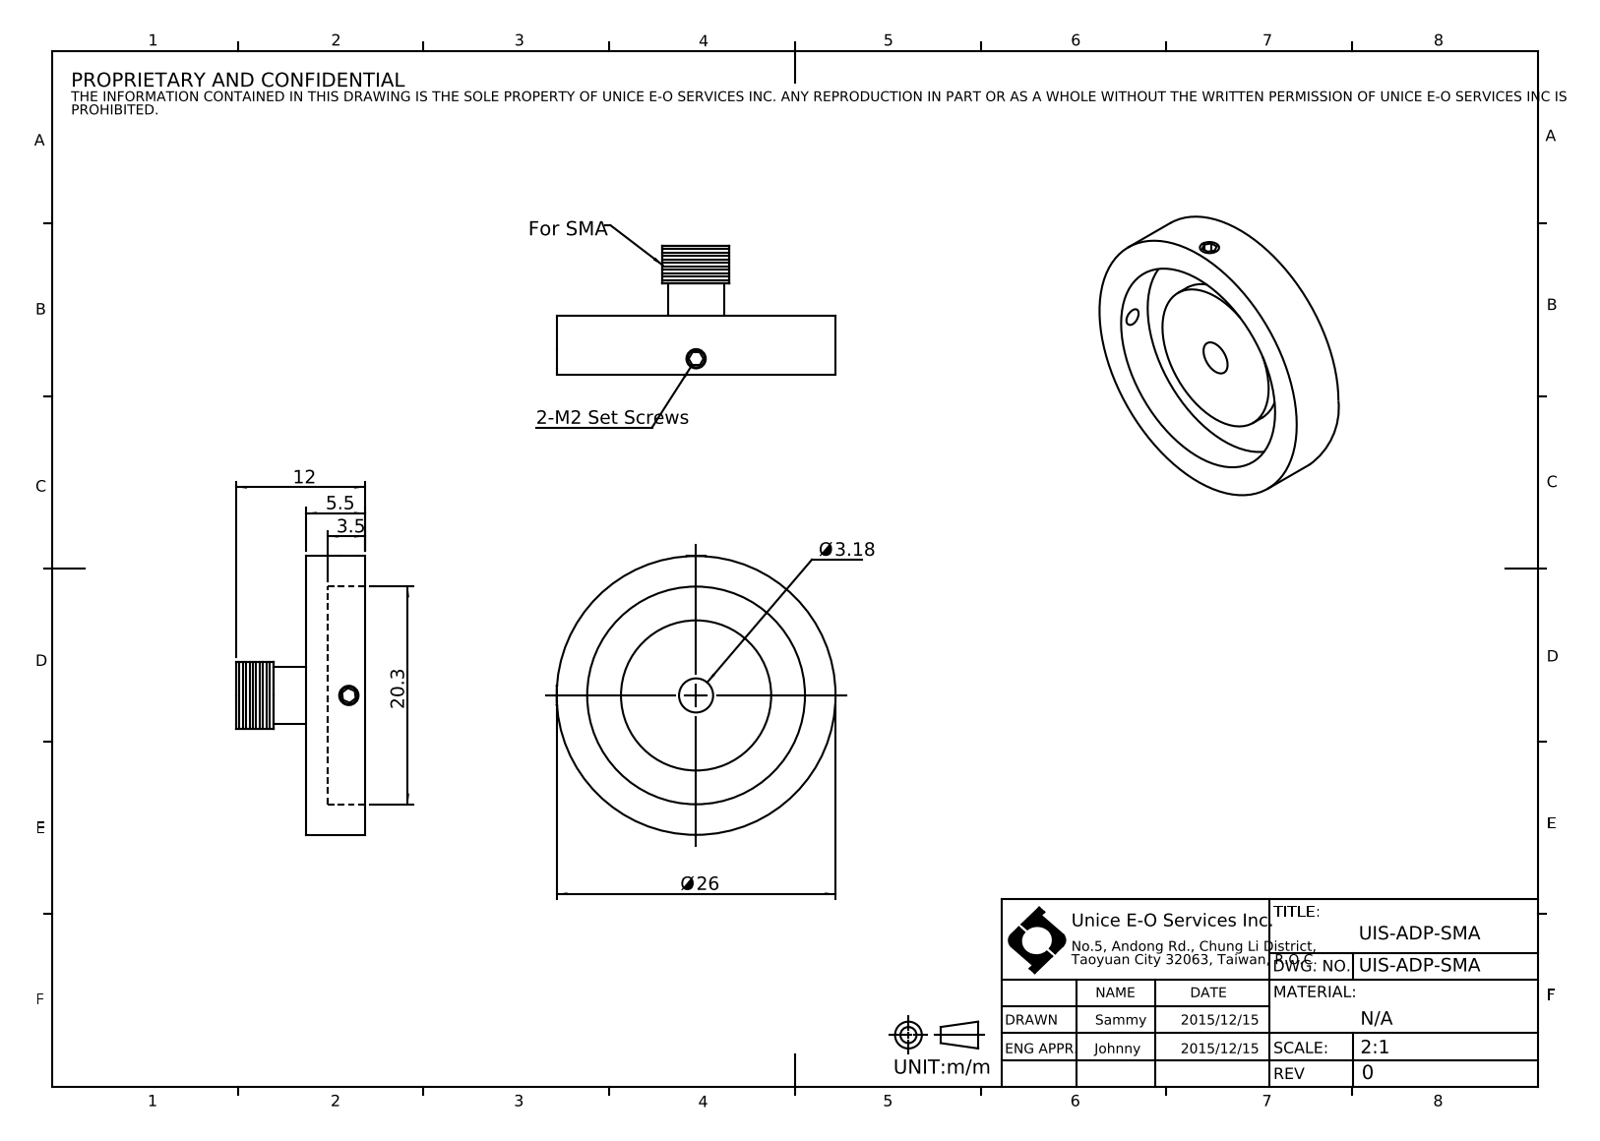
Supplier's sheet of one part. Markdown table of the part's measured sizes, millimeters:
| quantity | value |
| --- | --- |
| part name | UIS-ADP-SMA |
| STEP written by | SolidWorks 2015 (CONFIG_CONTROL_DESIGN) |
| units | millimeters |
| bodies | 3 solids, 38 faces (24 planar, 10 cylindrical, 4 other) |
| overall size | 26 × 26 × 12 |
| volume | 2 065 mm³ |
| surface area | 2 072 mm² |
| round holes (diameter × count) | 1.6 × 2, 3.18 × 1, 20.3 × 1 |
| round bosses / shafts (diameter × count) | 2 × 2, 26 × 1, 14 × 1, 6.22 × 1, 5.3 × 1 |
| main face-to-face distances | 5.5, 3.5, 2, 1.2, 3.2, 2.3, 8.5, 6.5, 9.7, 12 |
